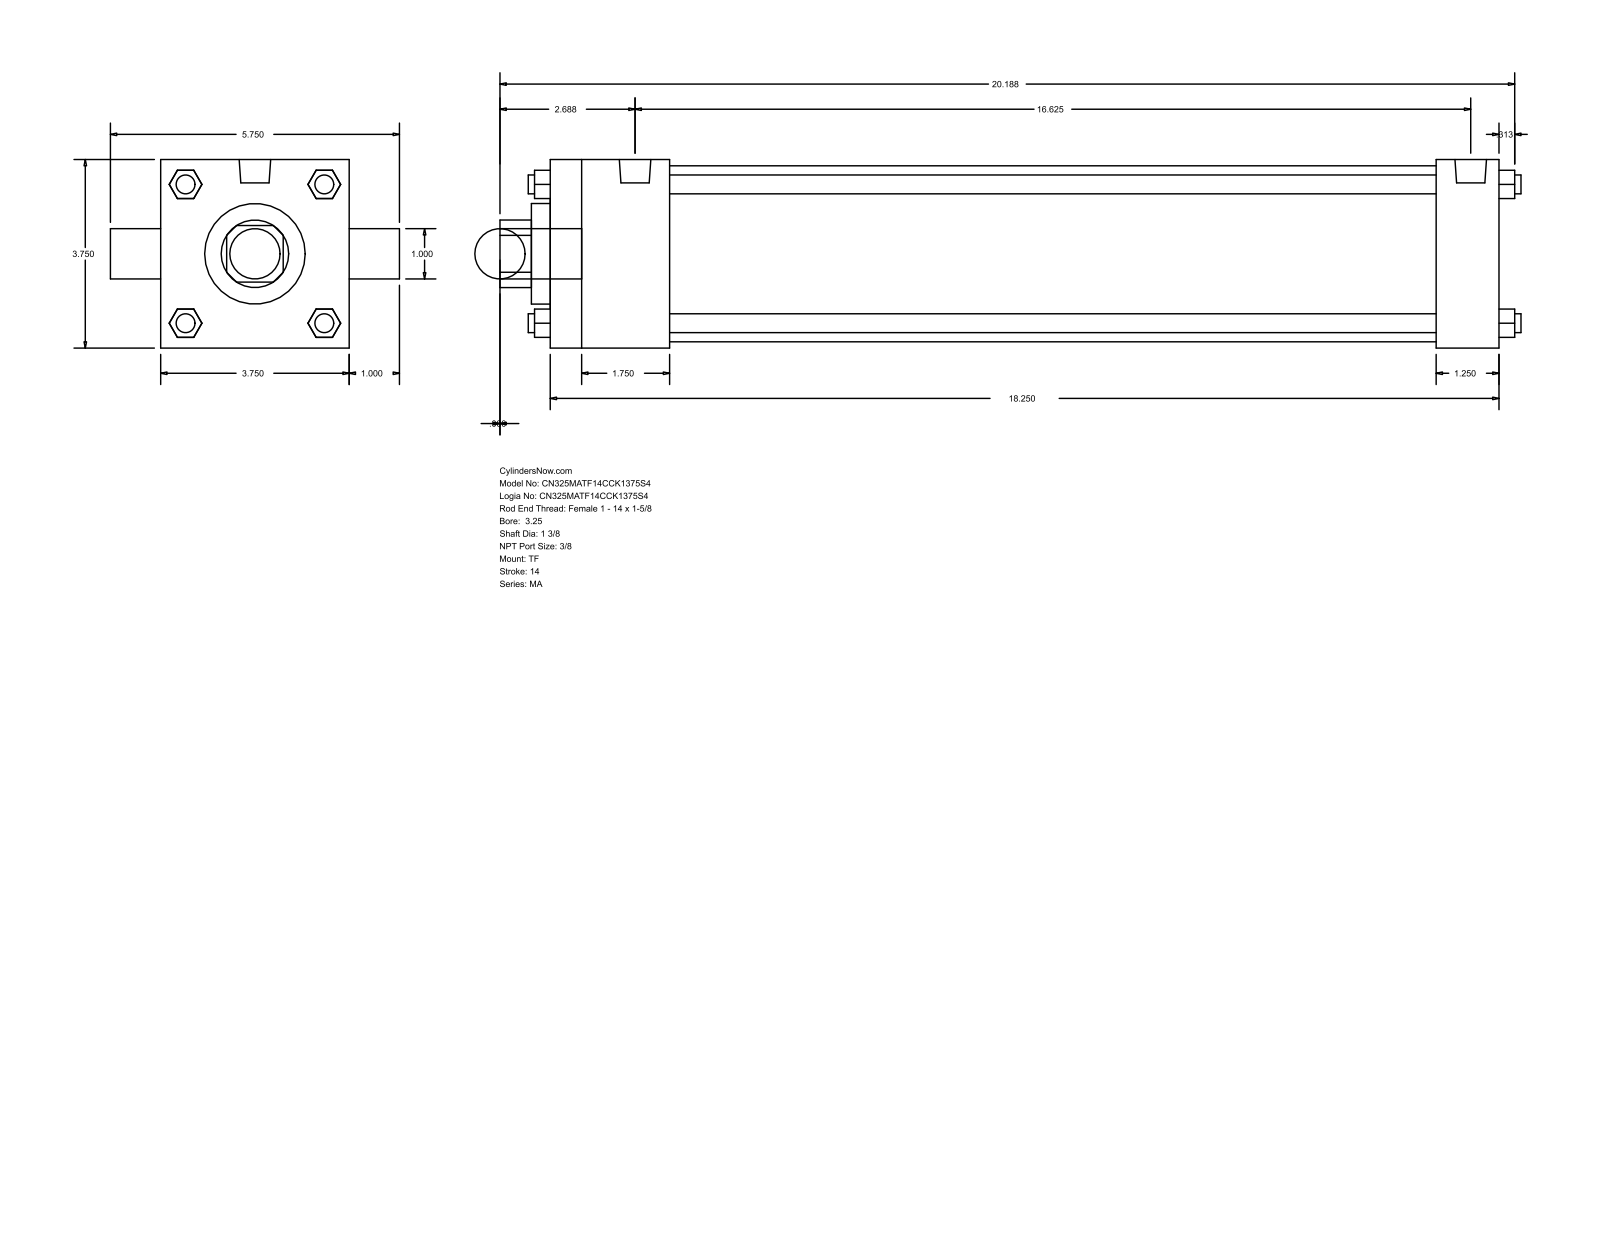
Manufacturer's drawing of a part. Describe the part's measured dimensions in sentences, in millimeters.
The part is named "MA_TF__0325_1.375". Its 3-D file was written by "GSSL Pune (CONFIG_CONTROL_DESIGN)". It is 0 solids with 120 faces: 92 planar, 28 cylindrical and 0 other. Overall it measures 515.94 by 146.05 by 95.25 millimeters. Round holes: 1 of diameter 25.4, 1 of diameter 34.92, 1 of diameter 50.8, 1 of diameter 88.9. Round bosses or shafts: 4 of diameter 9.53, 3 of diameter 11.11, 2 of diameter 15.93, 1 of diameter 25.4. Partial cylindrical surfaces (rounded edges, fillets, slot ends): 1 of radius 17.06. The main face-to-face distances are 95.24, 479.42, 60.32, 447.67, 387.35, 419.1, 31.75, 9.52, 69.84, 457.19.
